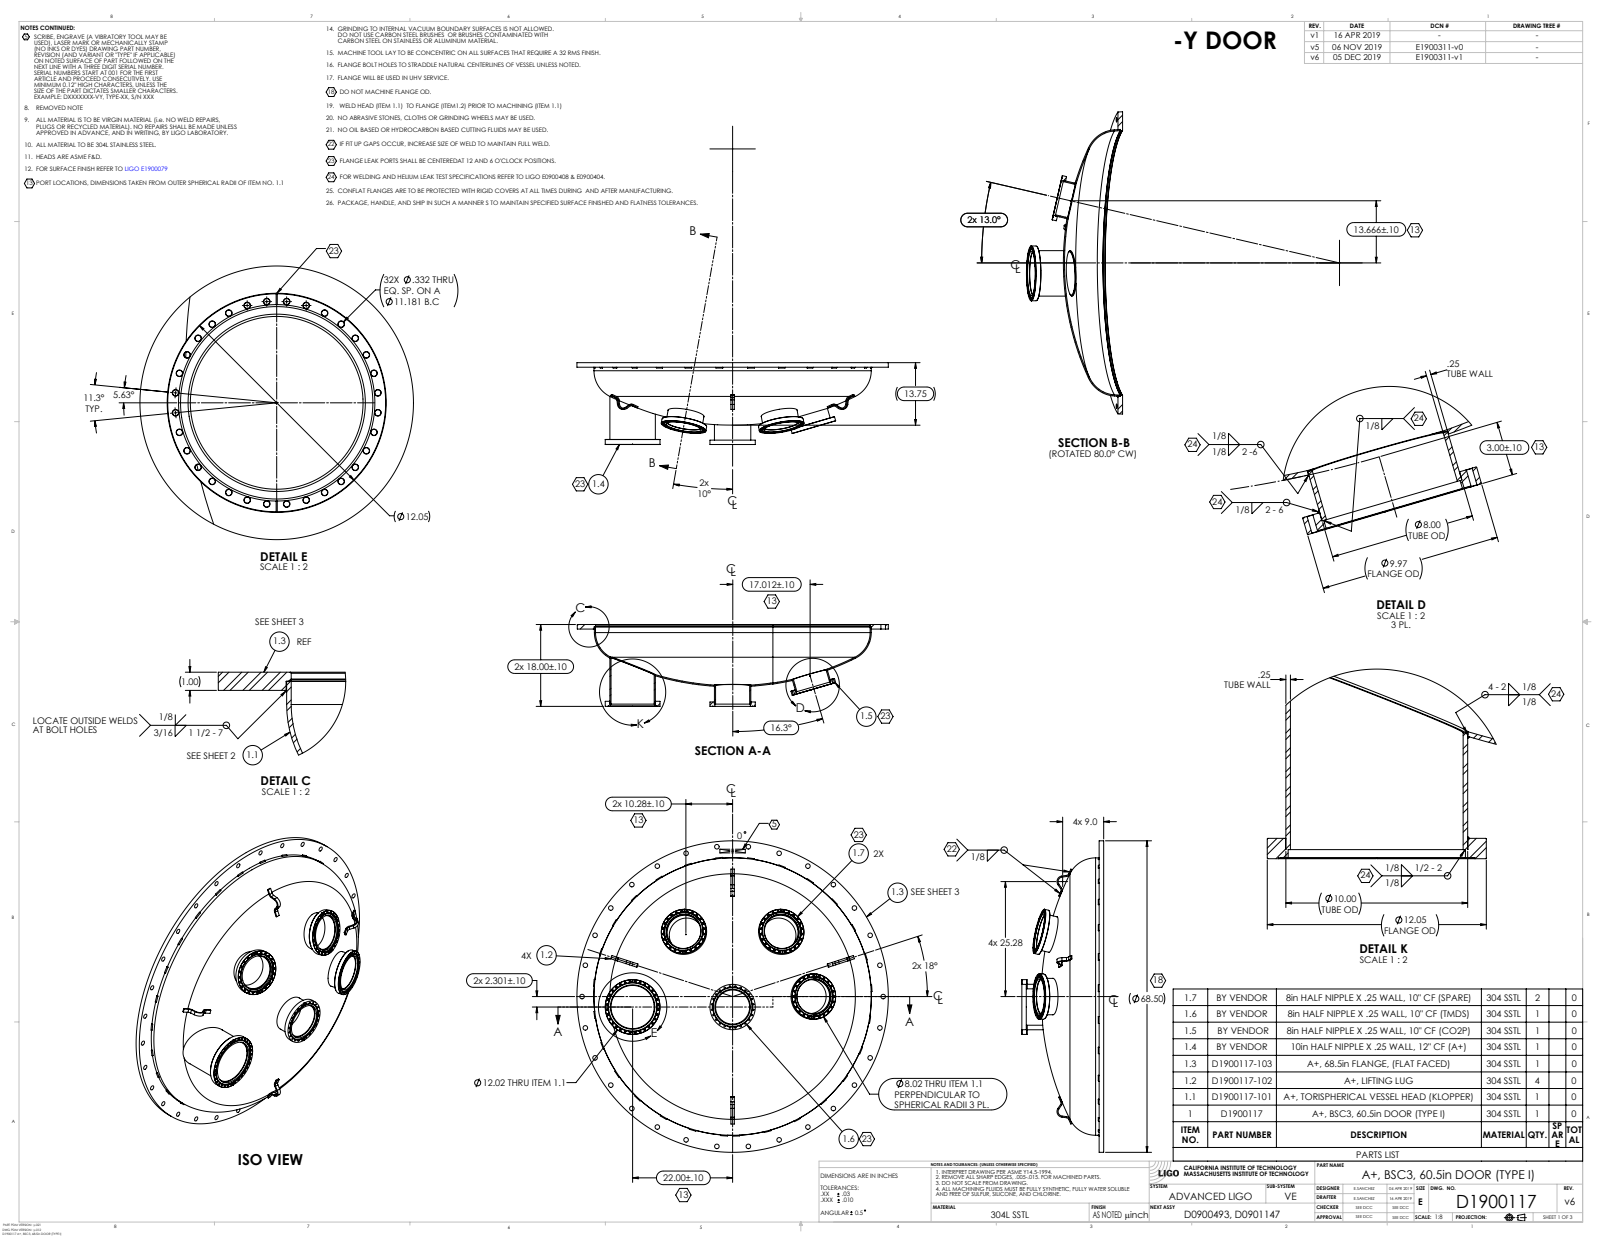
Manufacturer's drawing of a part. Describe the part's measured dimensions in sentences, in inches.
The part is named "D1900117-v6 A+, BSC3, 60.5in DOOR (TYPE I)". Its 3-D file was written by "SolidWorks 2019 (AUTOMOTIVE_DESIGN)". It is 41 solids with 778 faces: 225 planar, 282 cylindrical and 271 other. Overall it measures 68.5 by 68.5 by 18 inches. Its volume is 1 950 cubic inches and its surface area 11 463 square inches. Round holes: 128 of diameter 0.332, 30 of diameter 1, 5 of diameter 8.02, 4 of diameter 7.5, 4 of diameter 7.812, 4 of diameter 8.75, 3 of diameter 8.04, 3 of diameter 8.54, 1 of diameter 9.5, 1 of diameter 9.75, 1 of diameter 10.02, 1 of diameter 10.024. Round bosses or shafts: 4 of diameter 9.97, 4 of diameter 8, 1 of diameter 68.5, 1 of diameter 61.06, 1 of diameter 12.047, 1 of diameter 10. Partial cylindrical surfaces (rounded edges, fillets, slot ends): 8 of radius 0.625, 8 of radius 0.875, 4 of radius 1, 4 of radius 1.25. The main face-to-face distances are 1, 0.5, 17.5, 17, 0.97, 18, 0.05, 16.88, 16.38, 15.88. The hole center spacings are 4.564, 4.564, 2.363, 7.905, 1.191, 9.05, 7.242, 3.493.
